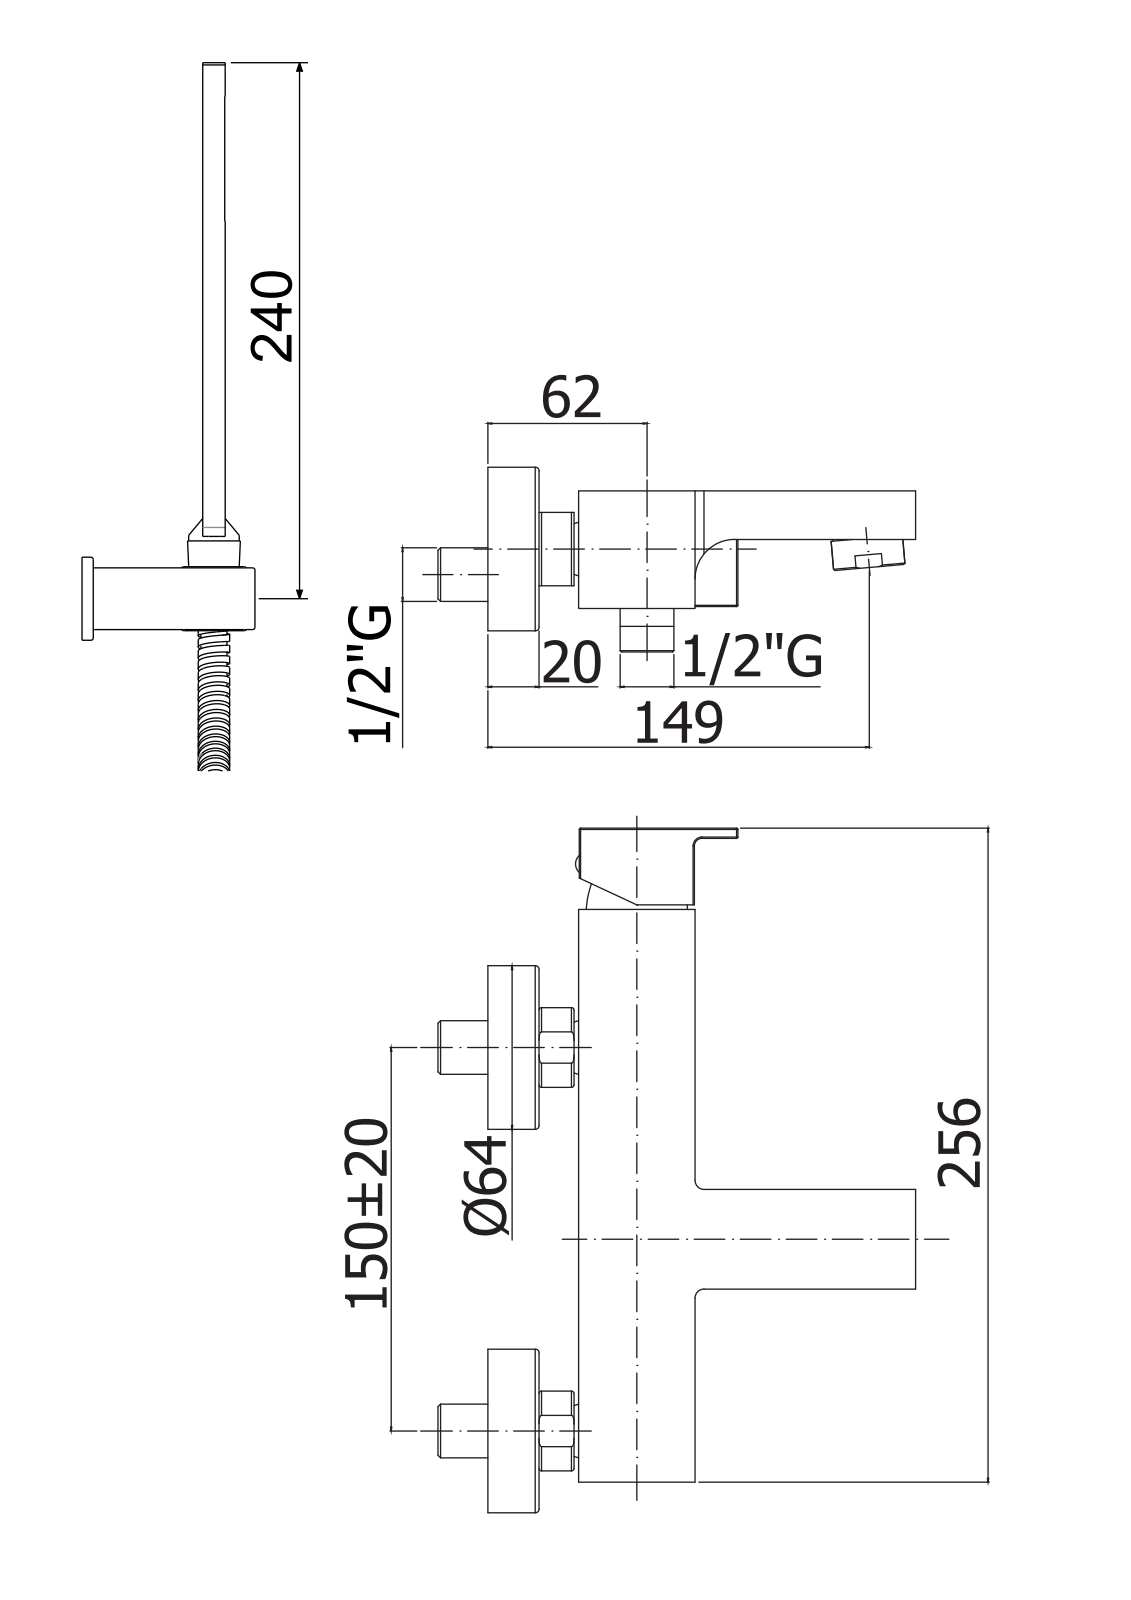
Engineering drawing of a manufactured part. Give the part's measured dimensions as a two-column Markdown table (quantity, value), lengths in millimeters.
| quantity | value |
| --- | --- |
| part name | EF023CR |
| STEP written by | CREO PARAMETRIC BY PTC INC, 2020044 (CONFIG_CONTROL_DESIGN) |
| units | millimeters |
| bodies | 3 solids, 3379 faces (2534 planar, 492 cylindrical, 353 other) |
| overall size | 475.25 × 387.5 × 168.25 |
| volume | 497 697 mm³ |
| surface area | 254 919 mm² |
| round holes (diameter × count) | 7 × 4, 24.5 × 3, 25 × 3, 4 × 2, 10.5 × 2, 12.7 × 2, 18 × 2, 21 × 2, 21.6 × 2, 28.5 × 2, 37 × 2, 62.3 × 2 |
| round bosses / shafts (diameter × count) | 2 × 11, 24 × 3, 63.5 × 2, 28 × 2, 27 × 2, 26.5 × 2, 17.7 × 2, 9.3 × 2 |
| partial cylindrical surfaces (radius × count) | 1 × 50, 0.5 × 49, 0.15 × 11, 0.3 × 8, 3 × 7, 4 × 3, 6.75 × 2, 15.6 × 2 |
| main face-to-face distances | 3.75, 42.75, 46.5, 3, 18.75, 39, 15, 0.75, 10, 24 |
| hole center spacings | 7.07, 8.6, 11.4, 1.17, 4, 6, 6.21, 7.44 |
